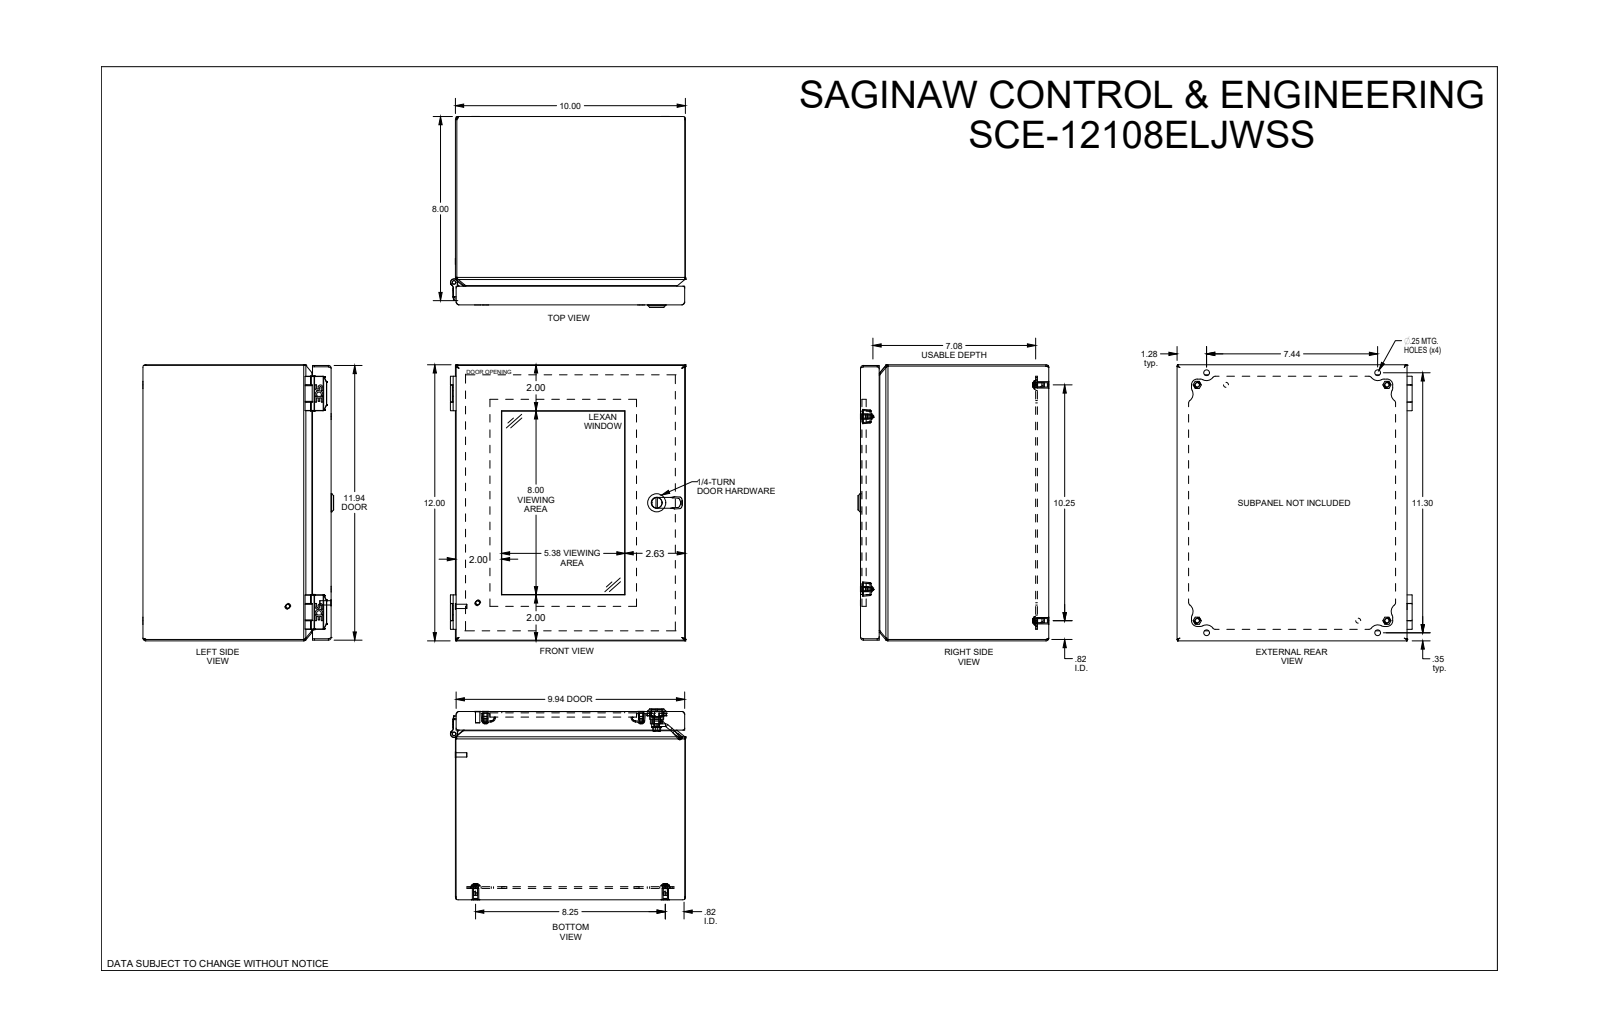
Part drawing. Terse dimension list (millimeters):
name: SCE-12108ELJW
written by: SolidWorks 2019 (AUTOMOTIVE_DESIGN)
unit: mm
bodies: 35 solids, 1094 faces (410 planar, 348 cylindrical, 336 other)
size: 306.3 × 259.6 × 210.7
volume: 956 300 mm³; area: 1 010 000 mm²
holes: 4× ⌀4.3, 4× ⌀4.8, 4× ⌀6.4, 4× ⌀7.2, 2× ⌀0.5, 2× ⌀2.5, 2× ⌀5.5, 2× ⌀6.8, 1× ⌀4, 1× ⌀5, 1× ⌀5.1, 1× ⌀6.1
bosses: 6× ⌀4.8, 4× ⌀12.2, 4× ⌀9.5, 4× ⌀7.1, 4× ⌀4.1, 2× ⌀6.6, 2× ⌀6.5, 2× ⌀6
rounds: 28× R0.8, 24× R0.6, 21× R0.3, 16× R1.3, 13× R6.4, 11× R3.2, 10× R0.3, 10× R1.5
face distances: 1.5, 254, 304.8, 1.5, 14.5, 13, 12.6, 11.1, 1.9, 206.4
hole spacings: 211.1, 241.3, 1.5, 31.8, 130.5, 177.8, 209.6, 238.7
